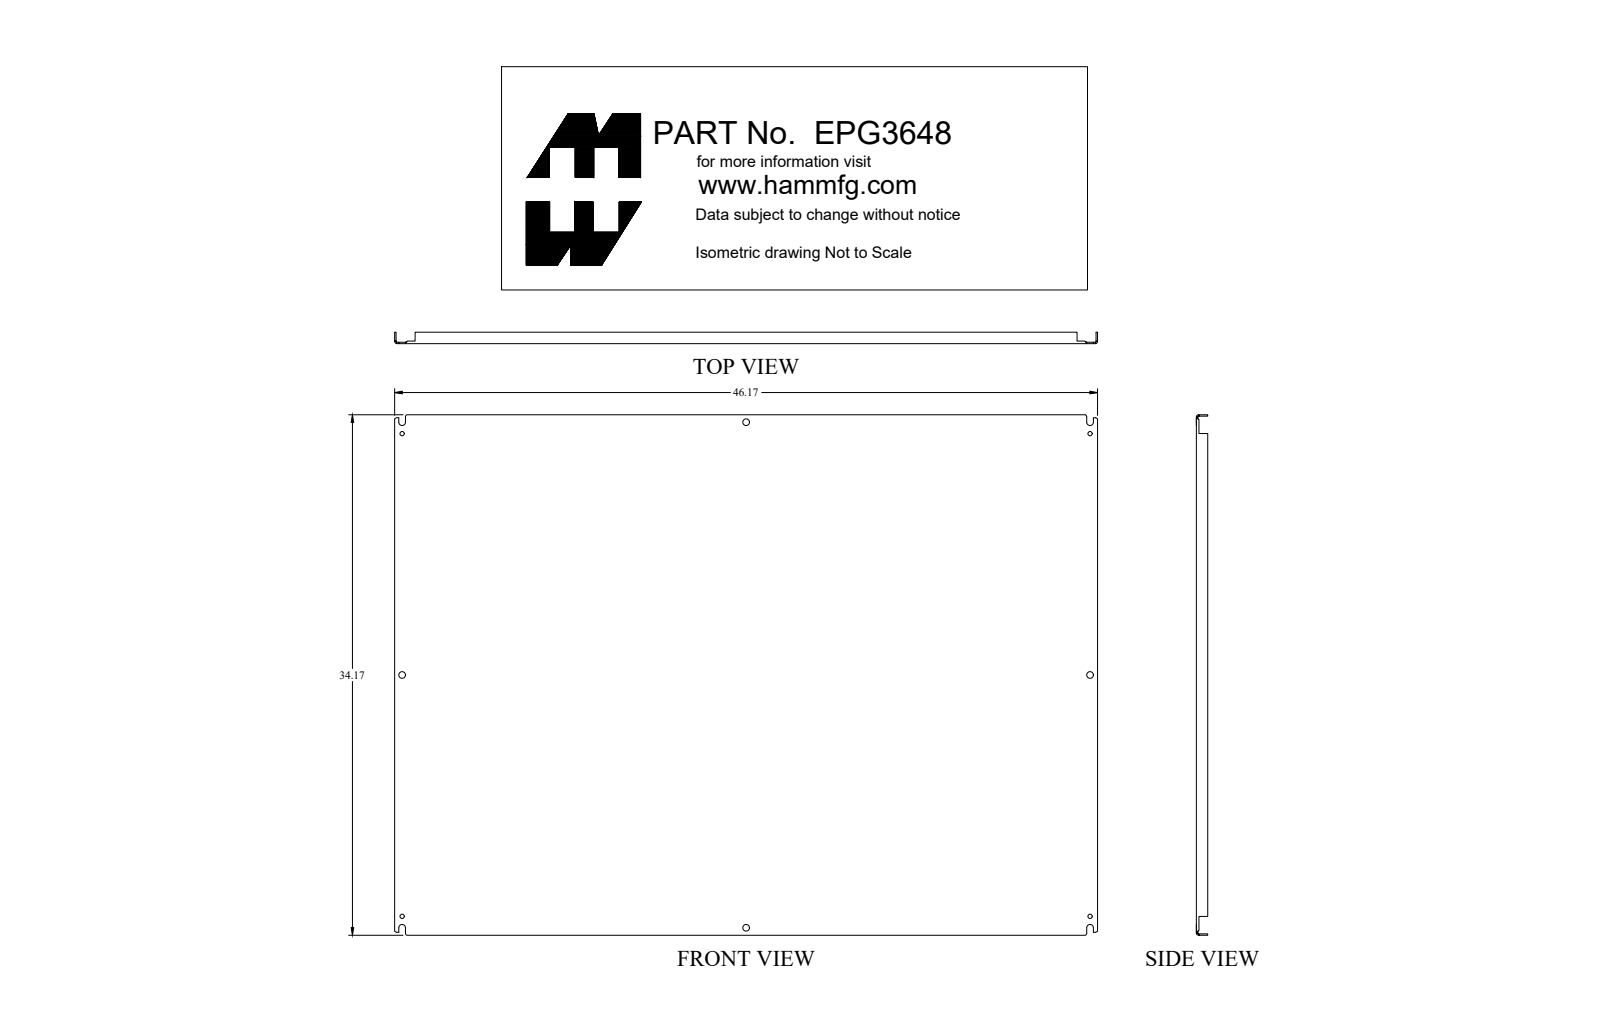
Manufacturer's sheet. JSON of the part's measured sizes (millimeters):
{"part_name": "EPG3648", "step_written_by": "SolidWorks 2018 (AUTOMOTIVE_DESIGN)", "units": "millimeters", "bodies": {"solids": 1, "faces": 136, "planar": 74, "cylindrical": 46, "other": 16}, "overall_size": [1172.7, 867.9, 19.1], "volume_mm3": 2596000, "surface_area_mm2": 2163000, "round_holes": [[7.1, 4], [11.1, 4]], "partial_cylinders_radius": [[1.2, 4], [1.6, 4], [3.6, 4], [5.6, 4]], "face_to_face_distances": [2.4, 865.5, 1170.3, 867.9, 863.1, 1167.9, 1172.7, 19.1, 16.6, 4.3], "hole_center_spacings": [402.4, 574.2, 712, 1004.1, 1216.3, 1147.8, 804.9, 1401.9]}
